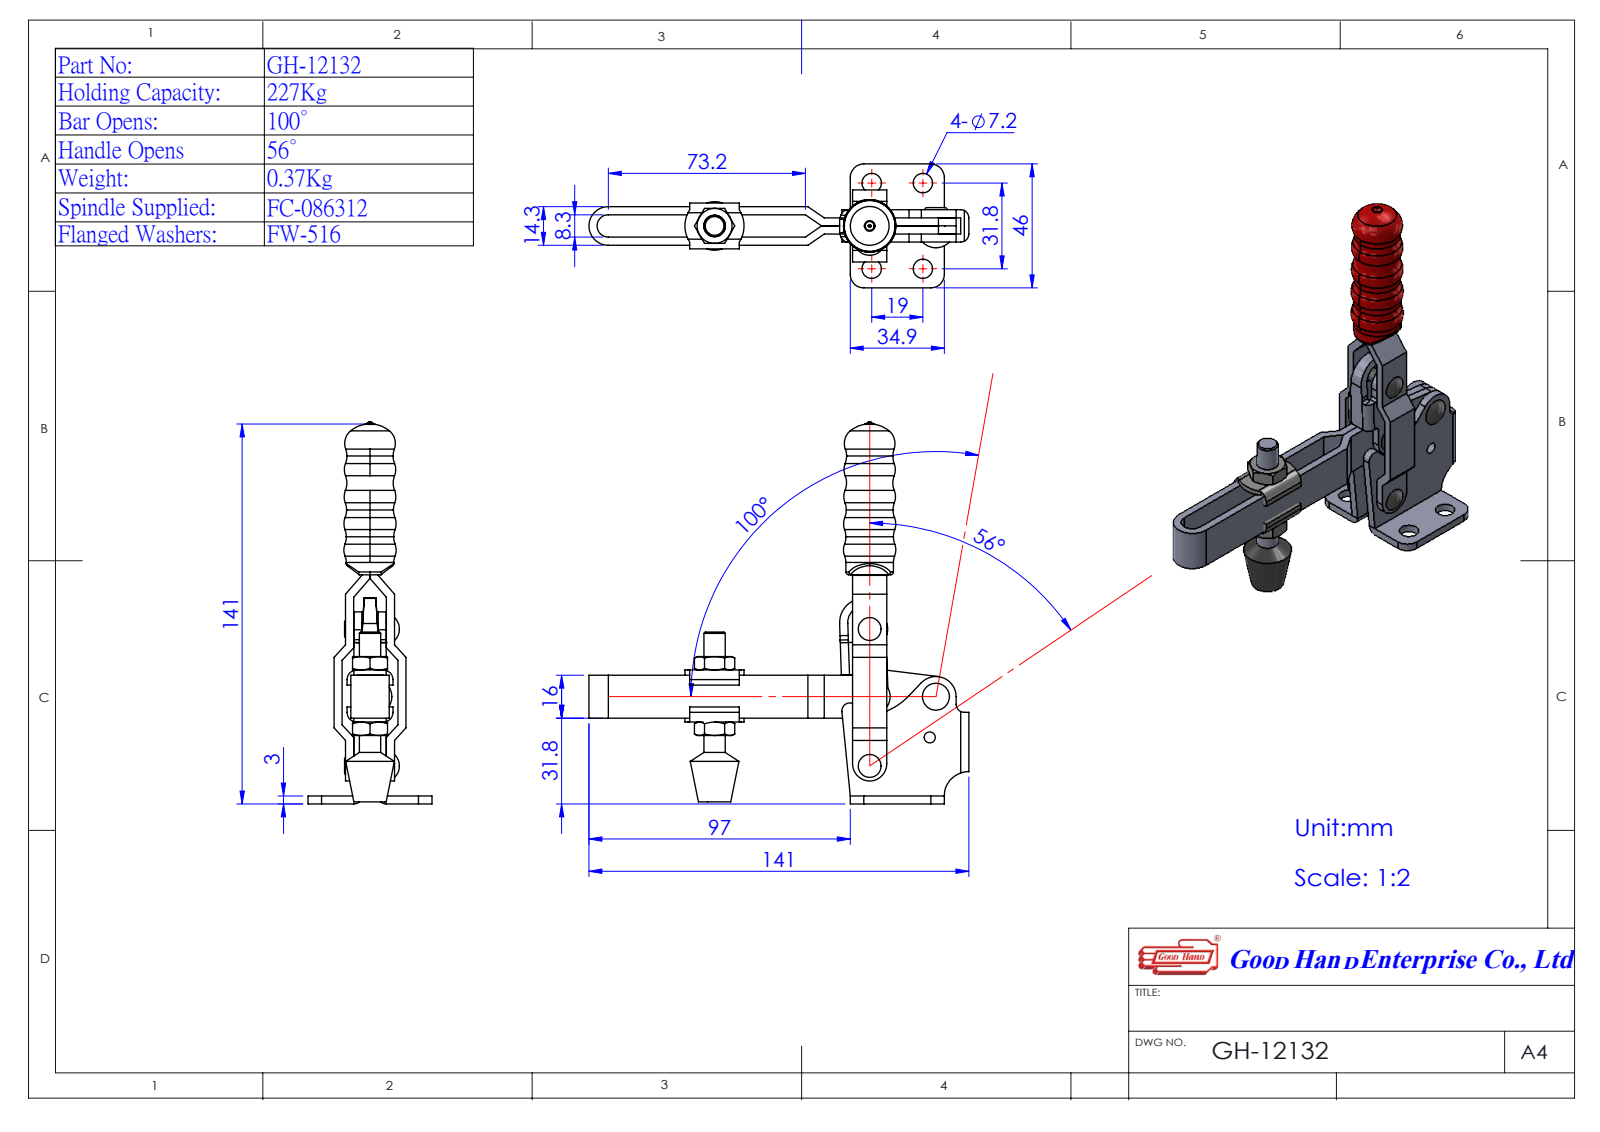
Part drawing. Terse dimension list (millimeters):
name: Group1^GH-12132(簡化); Group4^GH-12132(簡化); Group2^GH-12132(簡化); 11213208 (+2 more)
written by: SolidWorks 2016 (AUTOMOTIVE_DESIGN)
unit: mm
bodies: 5 solids, 325 faces (148 planar, 90 cylindrical, 87 other)
size: 141.16 × 141 × 46
volume: 59 035 mm³; area: 36 135 mm²
holes: 4× ⌀4, 4× ⌀7.2
bosses: 2× ⌀6.3, 1× ⌀17.61, 1× ⌀7.93
rounds: 4× R1.5, 4× R3, 4× R5, 4× R7.5, 2× R1, 2× R6.4, 2× R9, 1× R4.15
face distances: 3, 1.15, 10.15, 9, 6, 13.15, 1.85, 4.15, 11.3, 7.15
hole spacings: 19, 31.8, 37.04, 23.4, 25.13, 25.73, 35.14, 35.58
